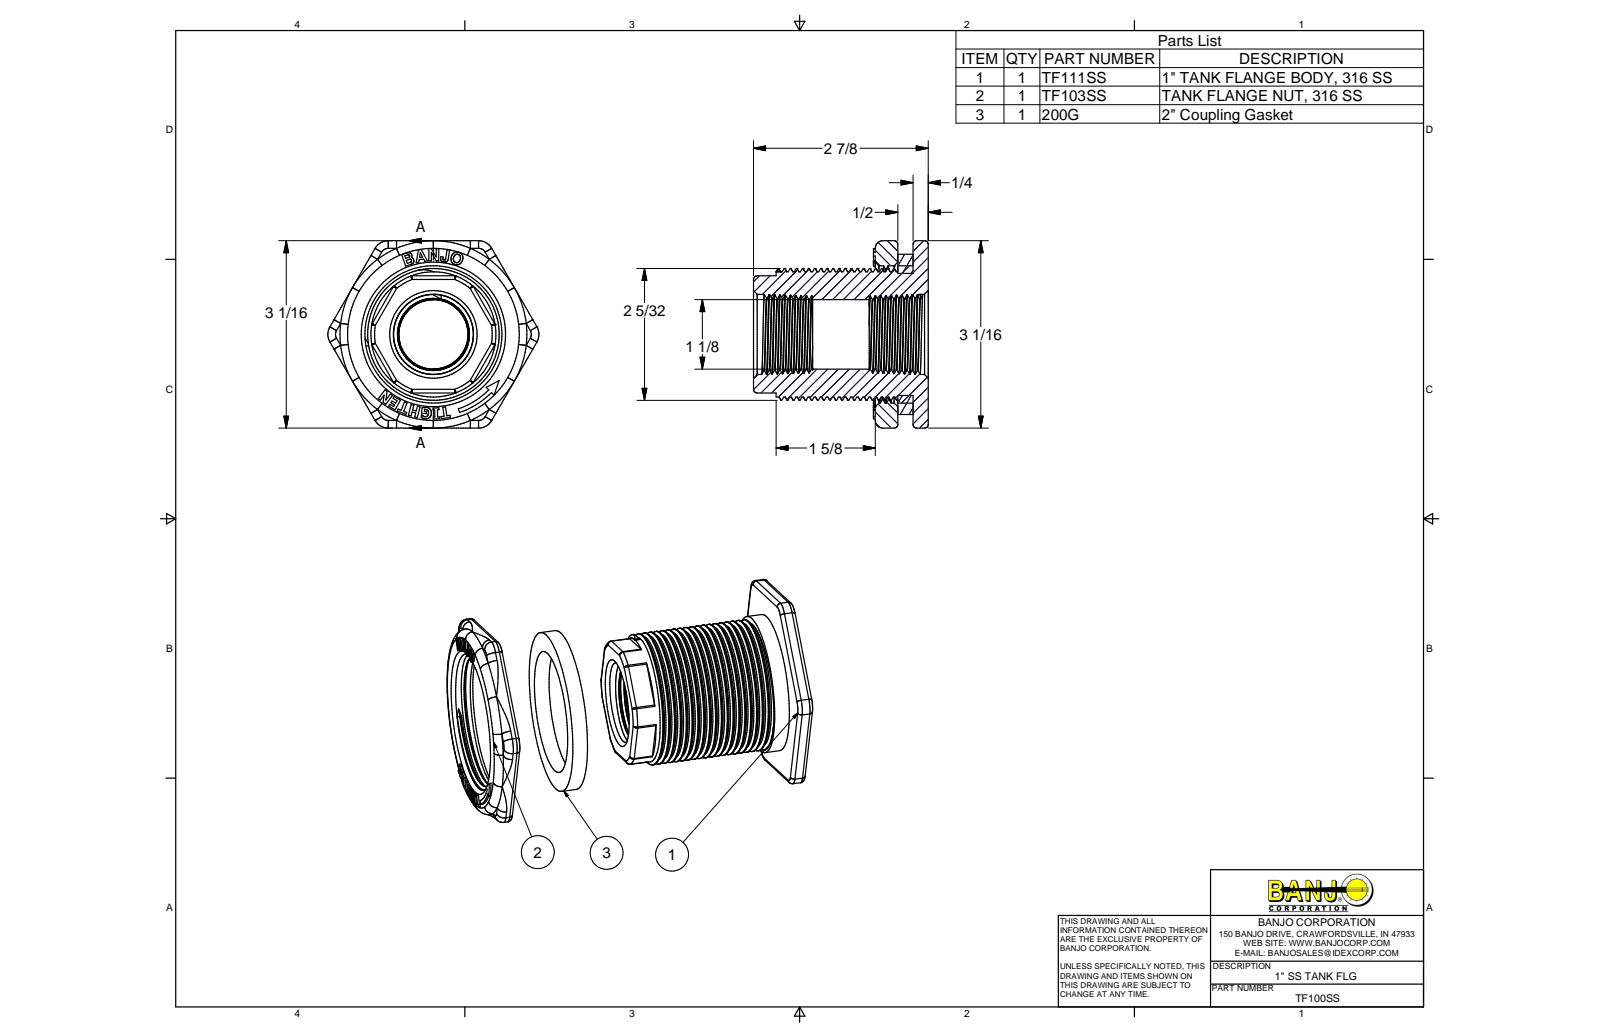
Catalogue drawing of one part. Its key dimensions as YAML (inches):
part_name: "TF100SS; TF111SS; TF103SS; 200G"
step_written_by: "Autodesk Inventor 2013 (AUTOMOTIVE_DESIGN)"
units: inches
bodies: {solids: 3, faces: 398, planar: 175, cylindrical: 72, other: 151}
overall_size: [3.468, 3.07, 2.87]
volume: 9.81
surface_area: 79.28
round_holes:
  - {diameter: 1.14, count: 1}
  - {diameter: 2, count: 1}
  - {diameter: 2.142, count: 1}
  - {diameter: 2.25, count: 1}
round_bosses_or_shafts:
  - {diameter: 2.625, count: 1}
  - {diameter: 2.16, count: 1}
  - {diameter: 2.052, count: 1}
partial_cylinders:
  - {radius: 0.06, count: 36}
  - {radius: 0.125, count: 6}
  - {radius: 0.25, count: 6}
  - {radius: 0.4, count: 1}
  - {radius: 1.286, count: 1}
  - {radius: 1.349, count: 1}
face_to_face_distances: [0.25, 0.5, 0.37, 0.62, 0.87, 2, 0.575, 2.495, 2.37, 2.62]
